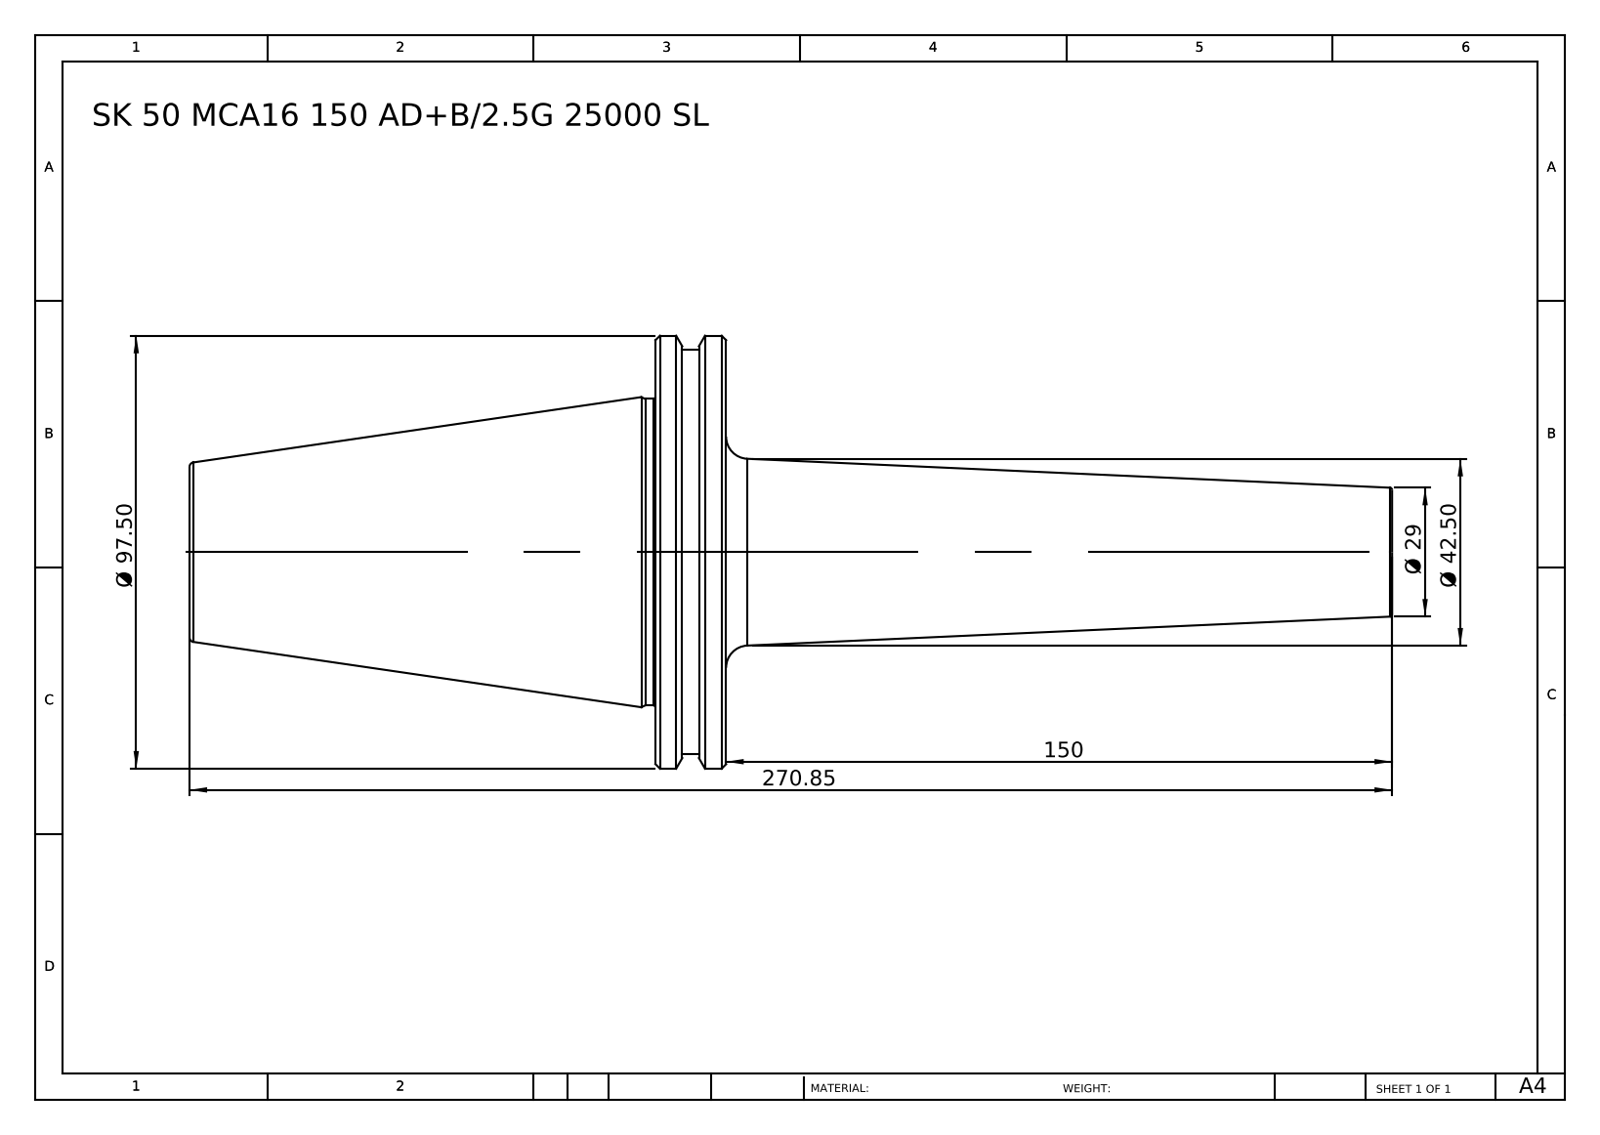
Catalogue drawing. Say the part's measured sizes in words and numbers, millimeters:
The part is named "SK 50 MCA16 150 AD+B-2.5G25000 SL". Its 3-D file was written by "SolidWorks 2014 (CONFIG_CONTROL_DESIGN)". It is 1 solid with 36 faces: 6 planar, 8 cylindrical and 22 other. Overall it measures 270.85 by 97.5 by 97.5 millimeters. Its volume is 526 575 cubic millimeters and its surface area 52 442 square millimeters. Round bosses or shafts: 1 of diameter 97.5, 1 of diameter 91, 1 of diameter 69. The main face-to-face distances are 15.9, 120.85, 104.95, 150, 165.9, 270.85, 156.13, 6.13, 9.77, 114.72.
